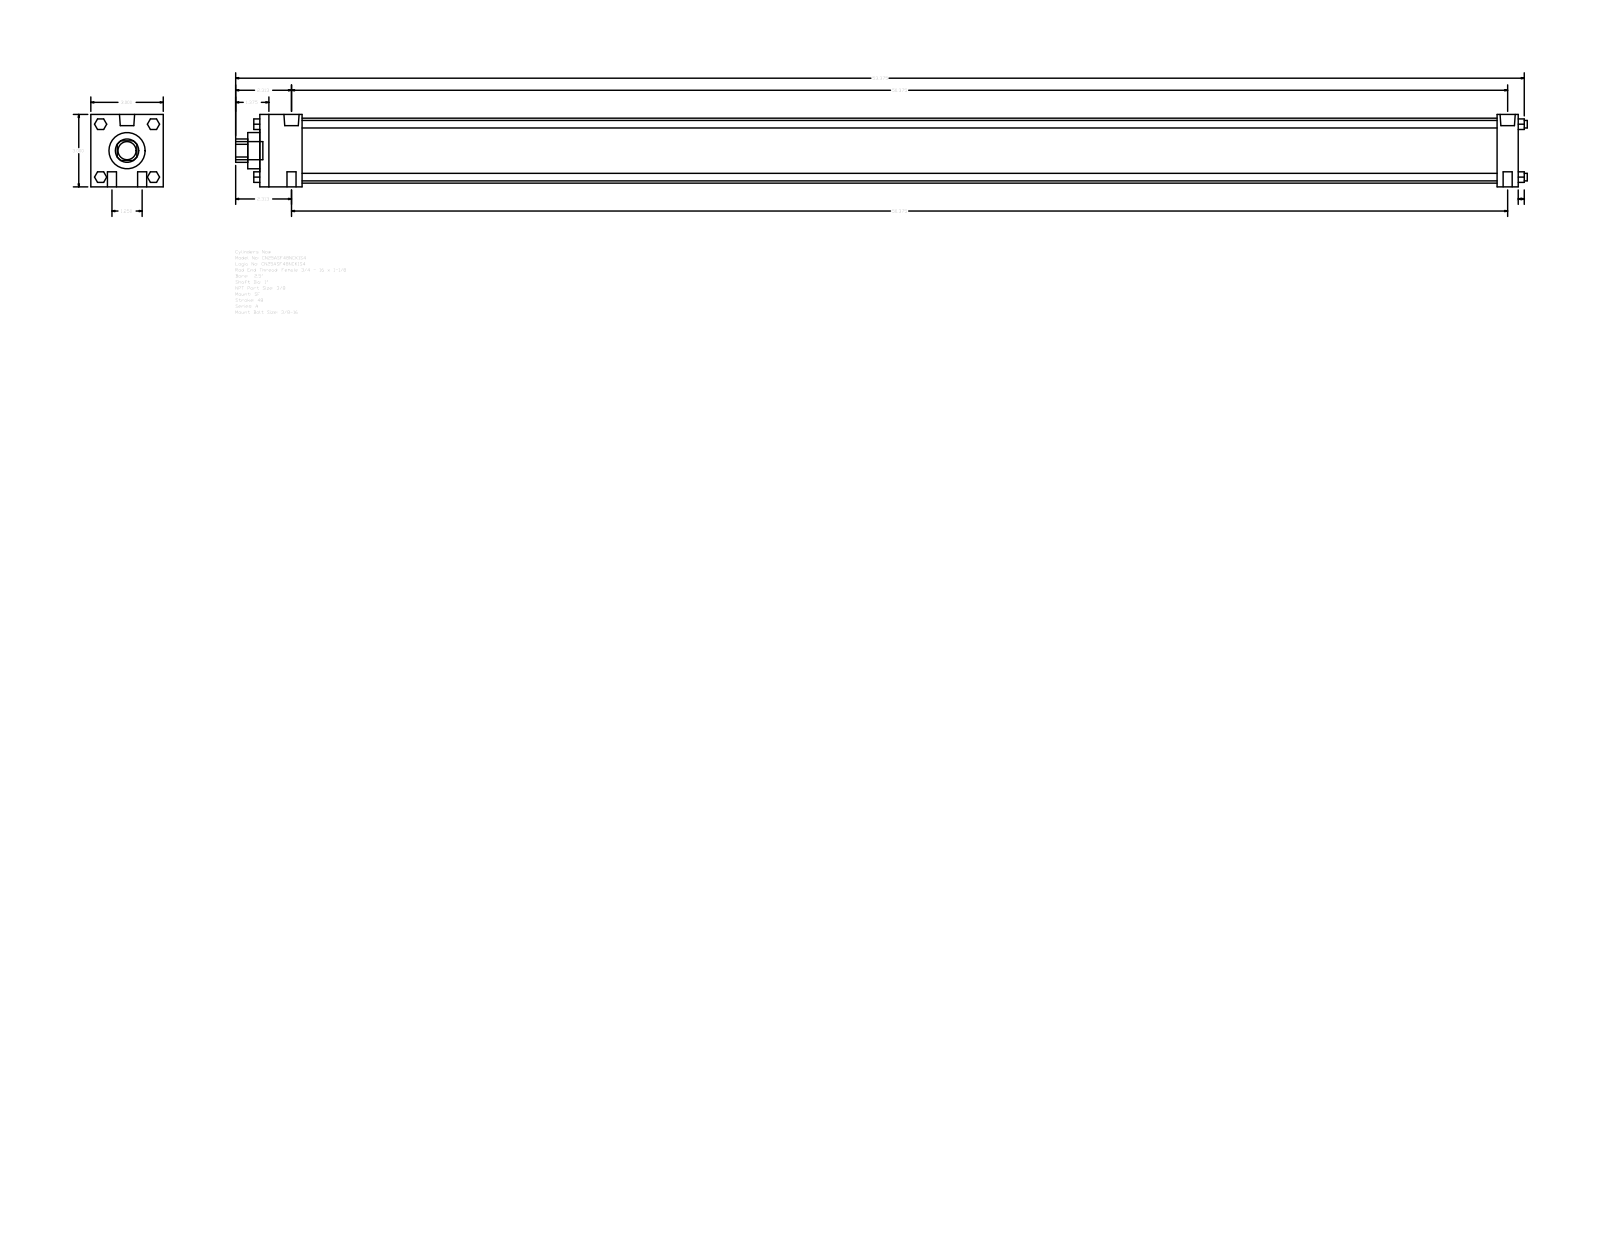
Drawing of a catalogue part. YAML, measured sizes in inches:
part_name: "A_SF__0250_1"
step_written_by: "GSSL Pune (CONFIG_CONTROL_DESIGN)"
units: inches
bodies: {solids: 0, faces: 124, planar: 94, cylindrical: 30, other: 0}
overall_size: [53.5, 3, 3]
round_holes:
  - {diameter: 1, count: 1}
  - {diameter: 1.5, count: 1}
  - {diameter: 2.69, count: 1}
round_bosses_or_shafts:
  - {diameter: 0.375, count: 4}
  - {diameter: 0.313, count: 4}
  - {diameter: 0.627, count: 2}
  - {diameter: 0.219, count: 2}
  - {diameter: 0.75, count: 1}
partial_cylinders:
  - {radius: 0.484, count: 1}
face_to_face_distances: [3, 52.125, 51.25, 0.875, 1.75, 49.5, 50.375, 0.5, 0.437, 2.25]
